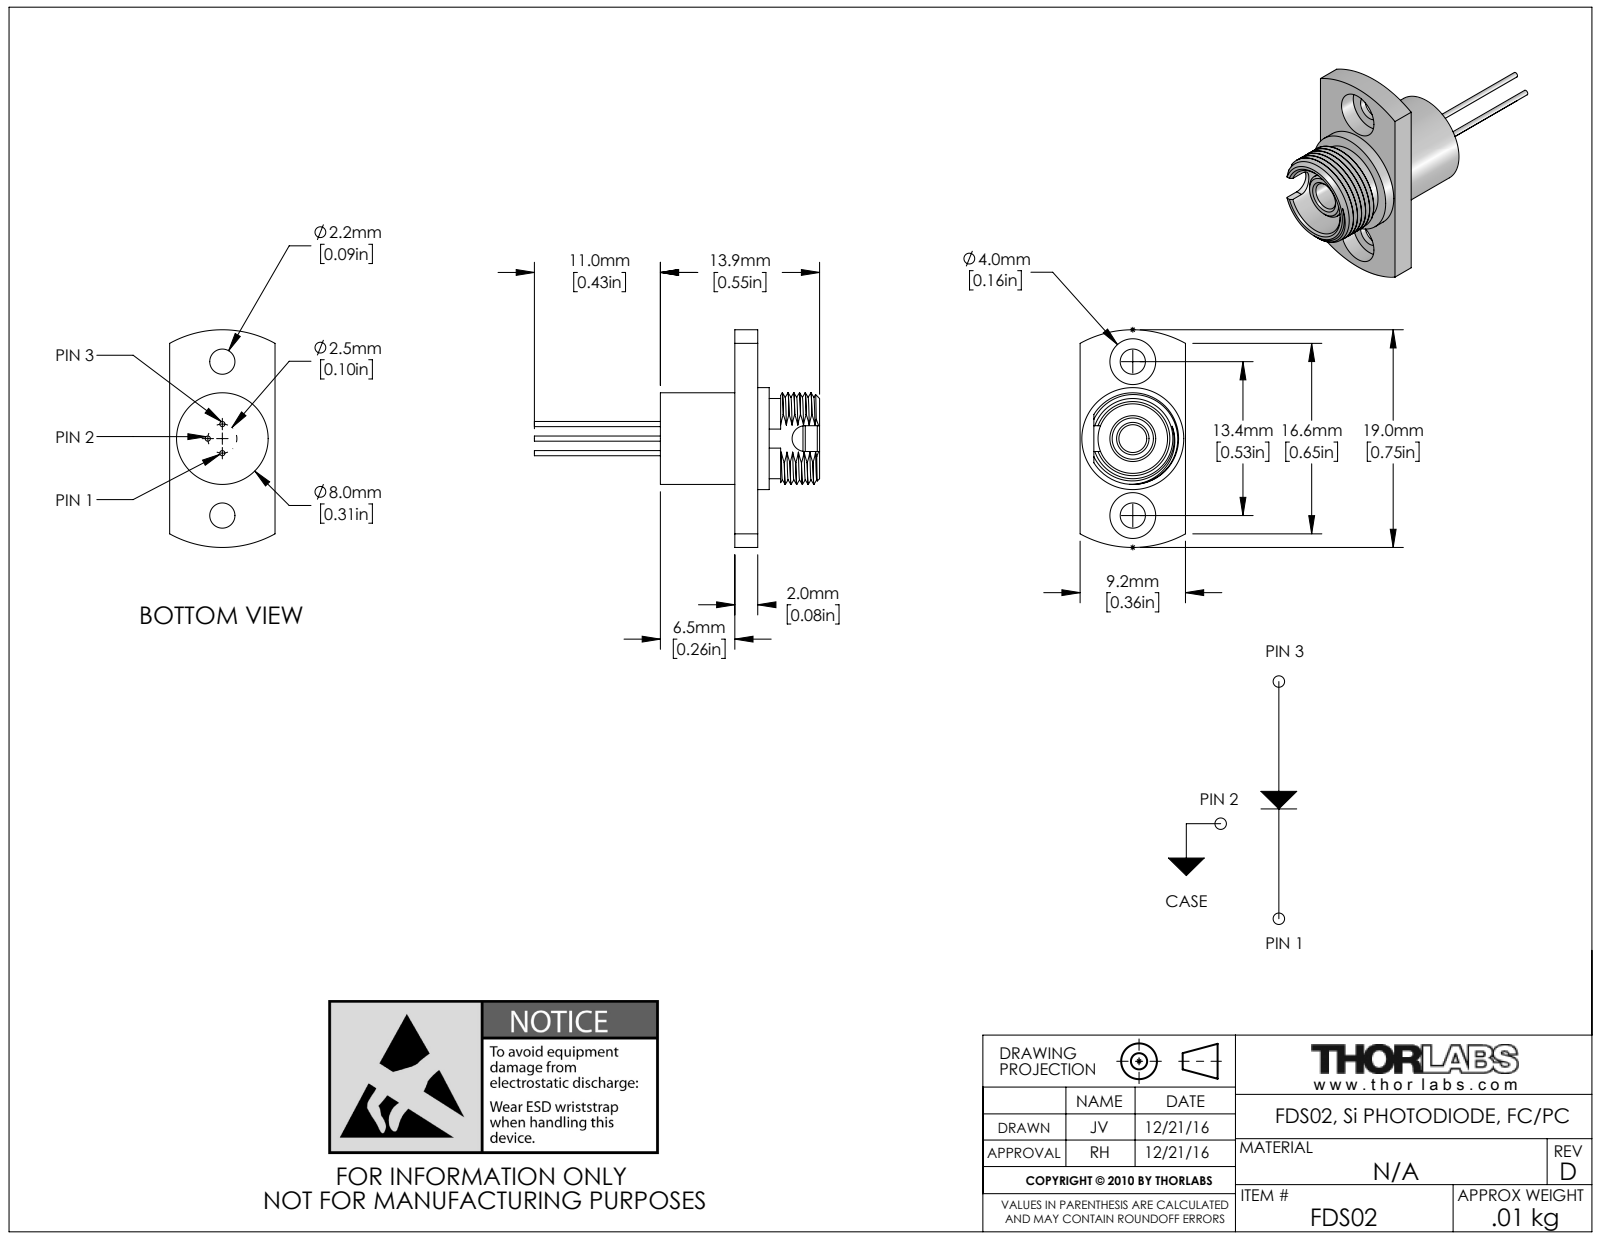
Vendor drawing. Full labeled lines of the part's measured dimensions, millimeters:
Part name (STEP PRODUCT): 16630-E0W
STEP written by: SolidWorks 2012 (AUTOMOTIVE_DESIGN)
Units: millimetres
Bodies: 1 solid, 77 faces (19 planar, 36 cylindrical, 22 other)
Overall size (bounding box): 24.9 × 19 × 9.2
Volume: 758 mm³ · Surface area: 1 035 mm²
Round holes (diameter × count): ⌀2.2 ×2, ⌀4 ×2, ⌀2.43 ×1, ⌀6.07 ×1
Round bosses / shafts (diameter × count): ⌀0.45 ×3, ⌀8.9 ×1, ⌀8 ×1, ⌀7 ×1, ⌀4 ×1
Partial cylindrical surfaces — rounded edges, fillets, slot ends (radius × count): R1.12 ×1, R9.5 ×1
Main face-to-face distances: 2, 6.5, 8.5, 1, 9.5, 3, 9.2, 7.05, 0.55, 1.45
Hole centre spacings: 6.71, 13.42
